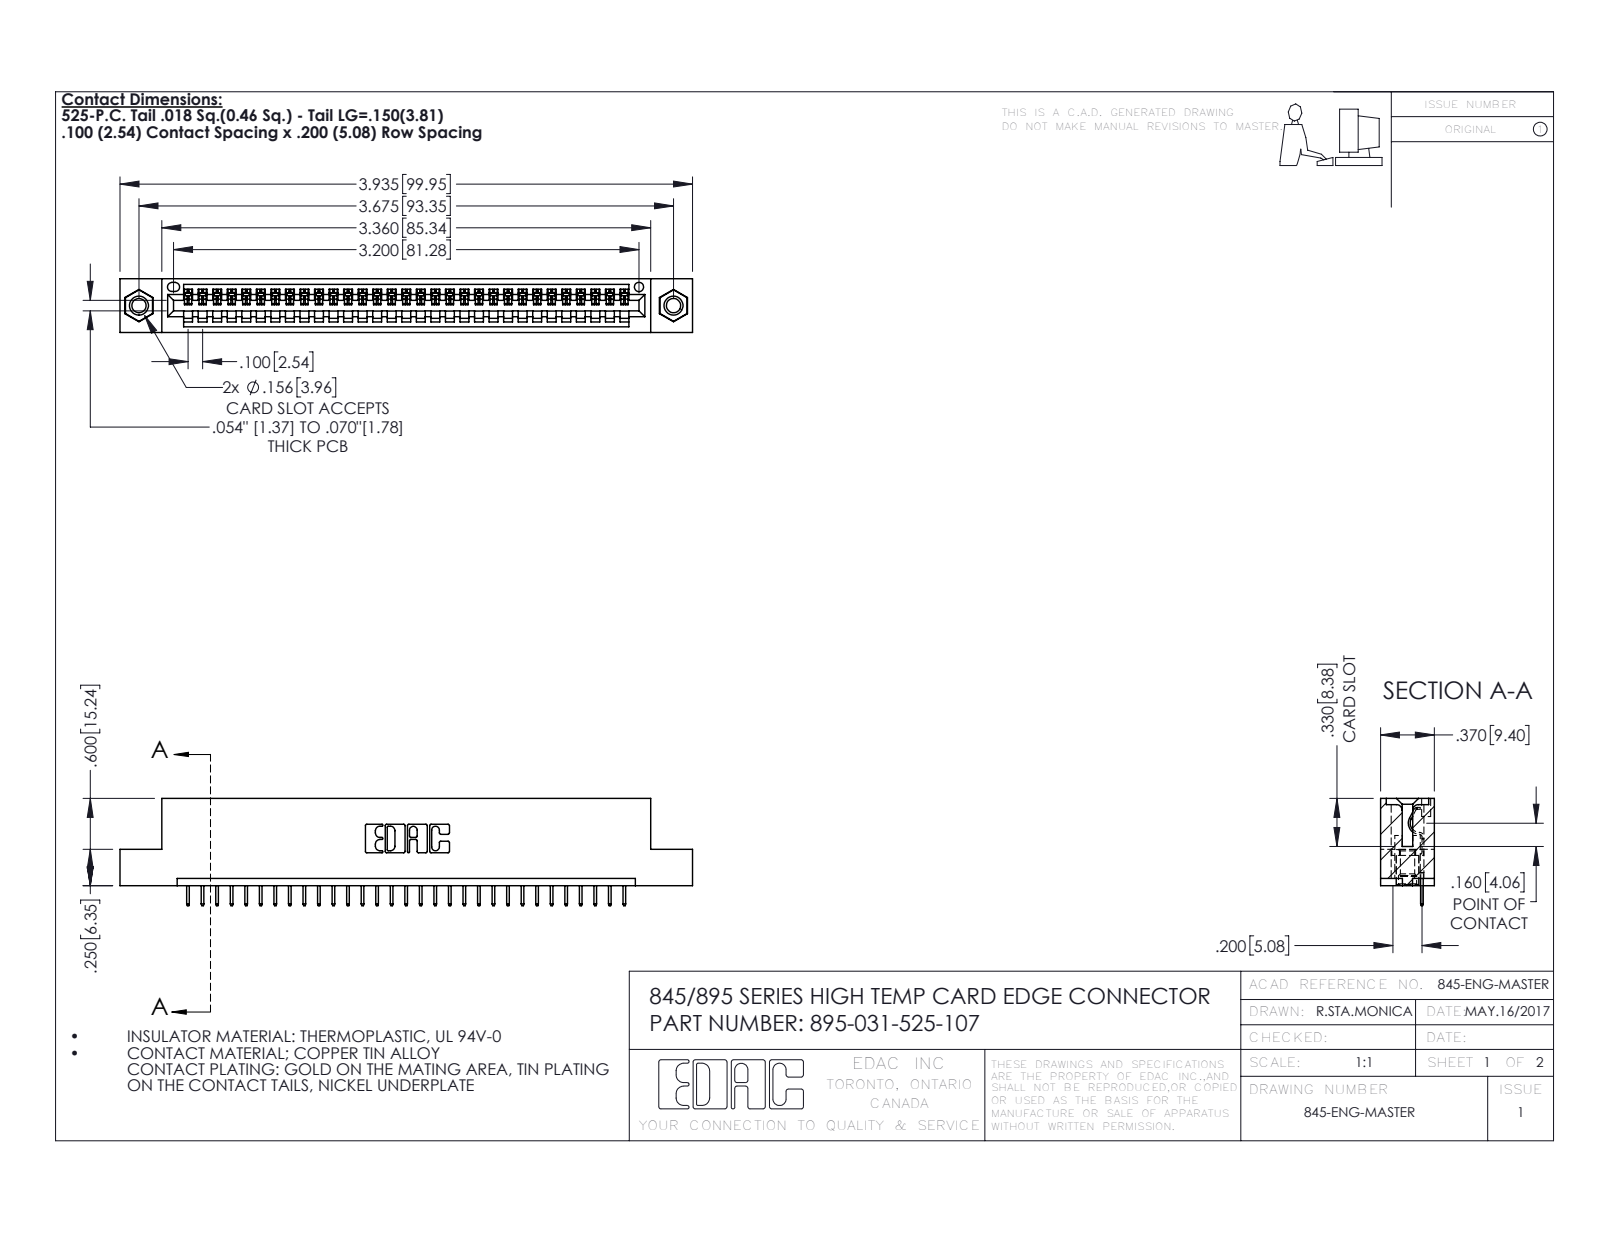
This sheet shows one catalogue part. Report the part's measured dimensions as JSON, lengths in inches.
{"part_name": "345-292-001_345-293-125; 345-250-001_345-250-005-103; 845 Part_Flush Mounting Lugs - 0.156 Dia-TI; 895-031-525-107", "step_written_by": "SolidWorks 2020 (CONFIG_CONTROL_DESIGN)", "units": "inches", "bodies": {"solids": 34, "faces": 2108, "planar": 1538, "cylindrical": 554, "other": 16}, "overall_size": [3.935, 0.737, 0.37], "volume_in3": 0.565, "surface_area_in2": 18.24, "round_holes": [[0.098, 2], [0.125, 2], [0.156, 2], [0.064, 1]], "round_bosses_or_shafts": [[0.155, 2]], "partial_cylinders_radius": [[0.006, 62], [0.01, 22], [0.007, 6], [0.031, 6], [0.026, 3], [0.031, 2], [0.04, 2], [0.014, 1]], "face_to_face_distances": [0.072, 0.298, 0.37, 0.2, 0.098, 0.272, 0.025, 0.225, 0.072, 0.149], "hole_center_spacings": [0.27, 3.44, 3.675]}
